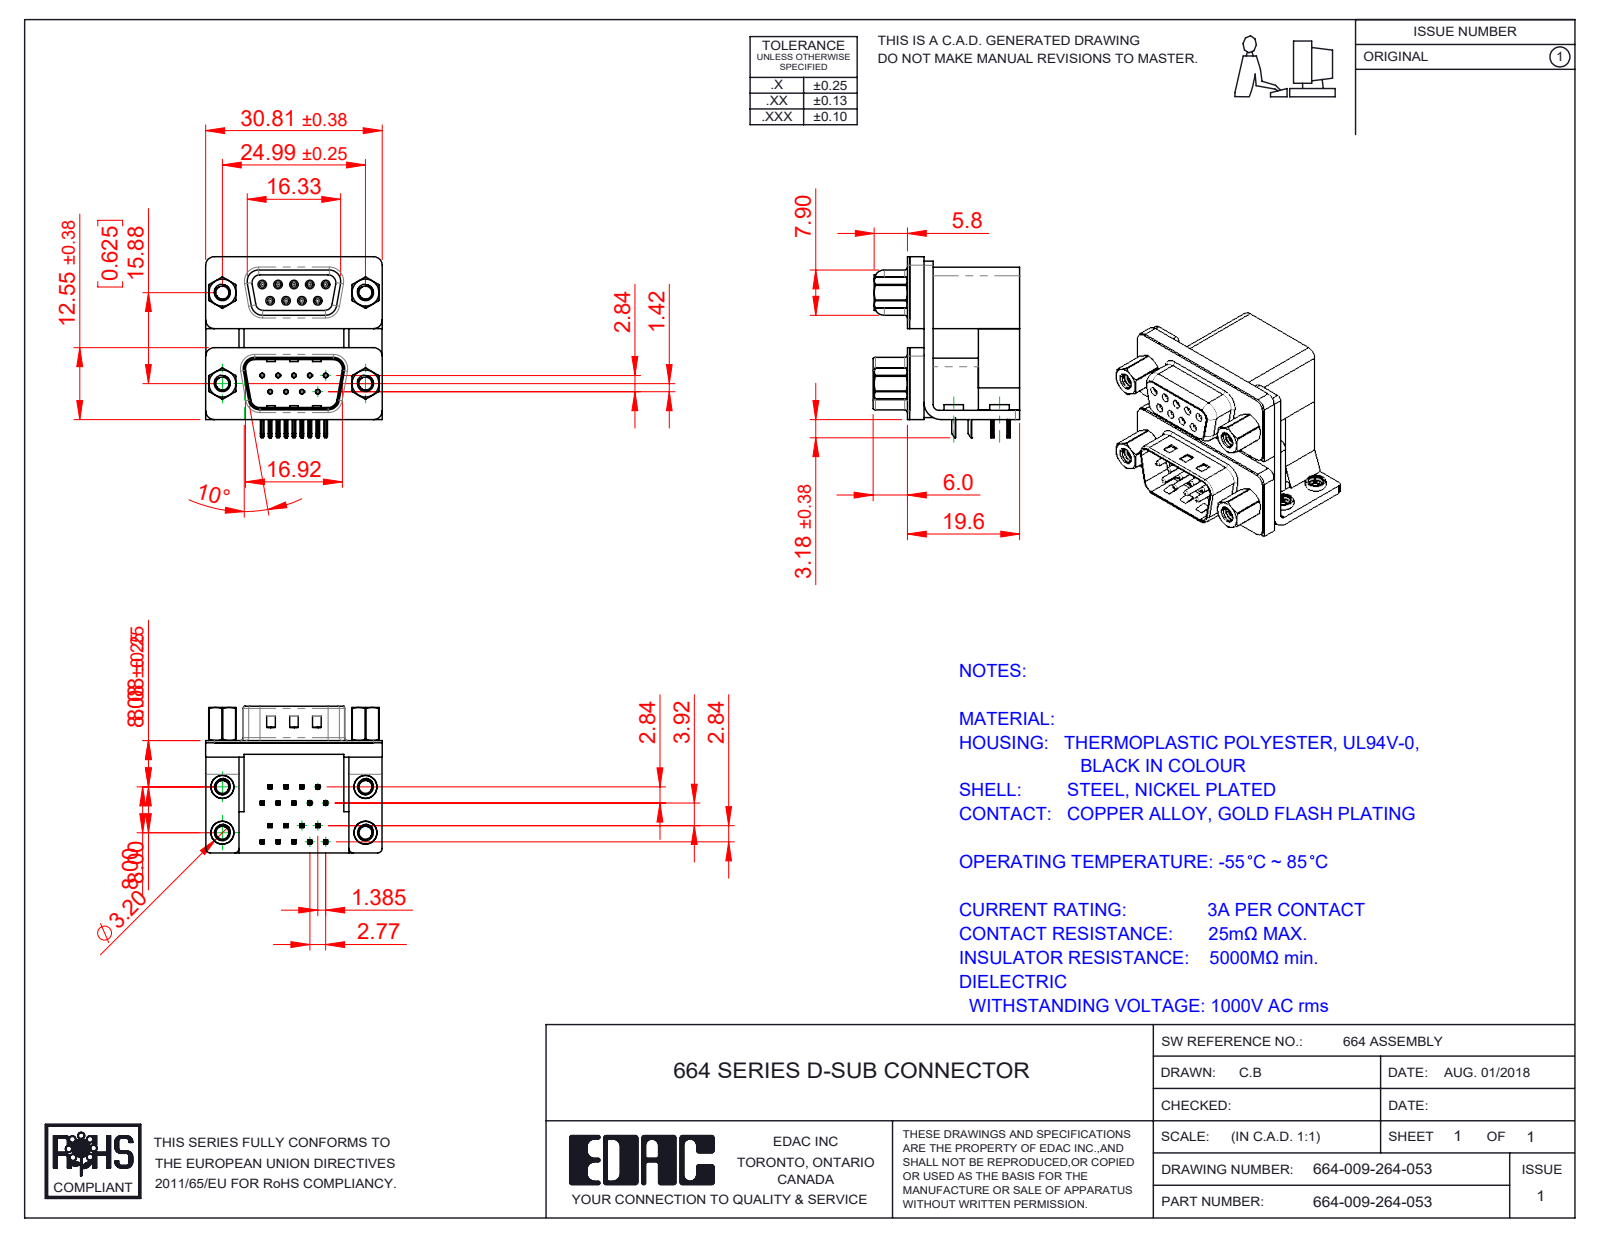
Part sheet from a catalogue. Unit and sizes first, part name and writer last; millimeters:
Units: millimetres
Overall size (bounding box): 31.61 × 30.81 × 25.6
Round holes (diameter × count): ⌀0.8 ×18, ⌀0.35 ×9, ⌀0.9 ×9, ⌀2.26 ×8, ⌀2.29 ×4, ⌀2.75 ×4, ⌀3.2 ×4, ⌀3.5 ×4, ⌀4 ×4, ⌀4.8 ×4, ⌀5 ×4
Round bosses / shafts (diameter × count): ⌀1.2 ×9, ⌀0.75 ×9, ⌀4.9 ×4, ⌀4.75 ×4, ⌀4 ×4, ⌀3.9 ×4, ⌀3.4 ×4, ⌀2.79 ×4
Partial cylindrical surfaces — rounded edges, fillets, slot ends (radius × count): R0.1 ×72, R0.15 ×36, R0.25 ×36, R0.12 ×18, R0.35 ×18, R1.5 ×13, R0.5 ×12, R1.35 ×10
Main face-to-face distances: 0.4, 2.5, 16.7, 19.2, 19.6, 2.9, 7.2, 9.5, 12, 12.4
Hole centre spacings: 3.16, 2.77, 16.12, 15.88, 5.54, 16.82, 24.99, 13.11
Volume: 10 783 mm³ · Surface area: 13 348 mm²
Bodies: 37 solids, 2921 faces (1319 planar, 915 cylindrical, 687 other)
Part name (STEP PRODUCT): 664 Housing Spacer_09 Contacts L; 664 4-40 Hex Standoff 5; 664 4-40 Threaded Board Mount; 664 Contact Top Upper_L (+8 more)
STEP written by: SolidWorks 2020 (CONFIG_CONTROL_DESIGN)
